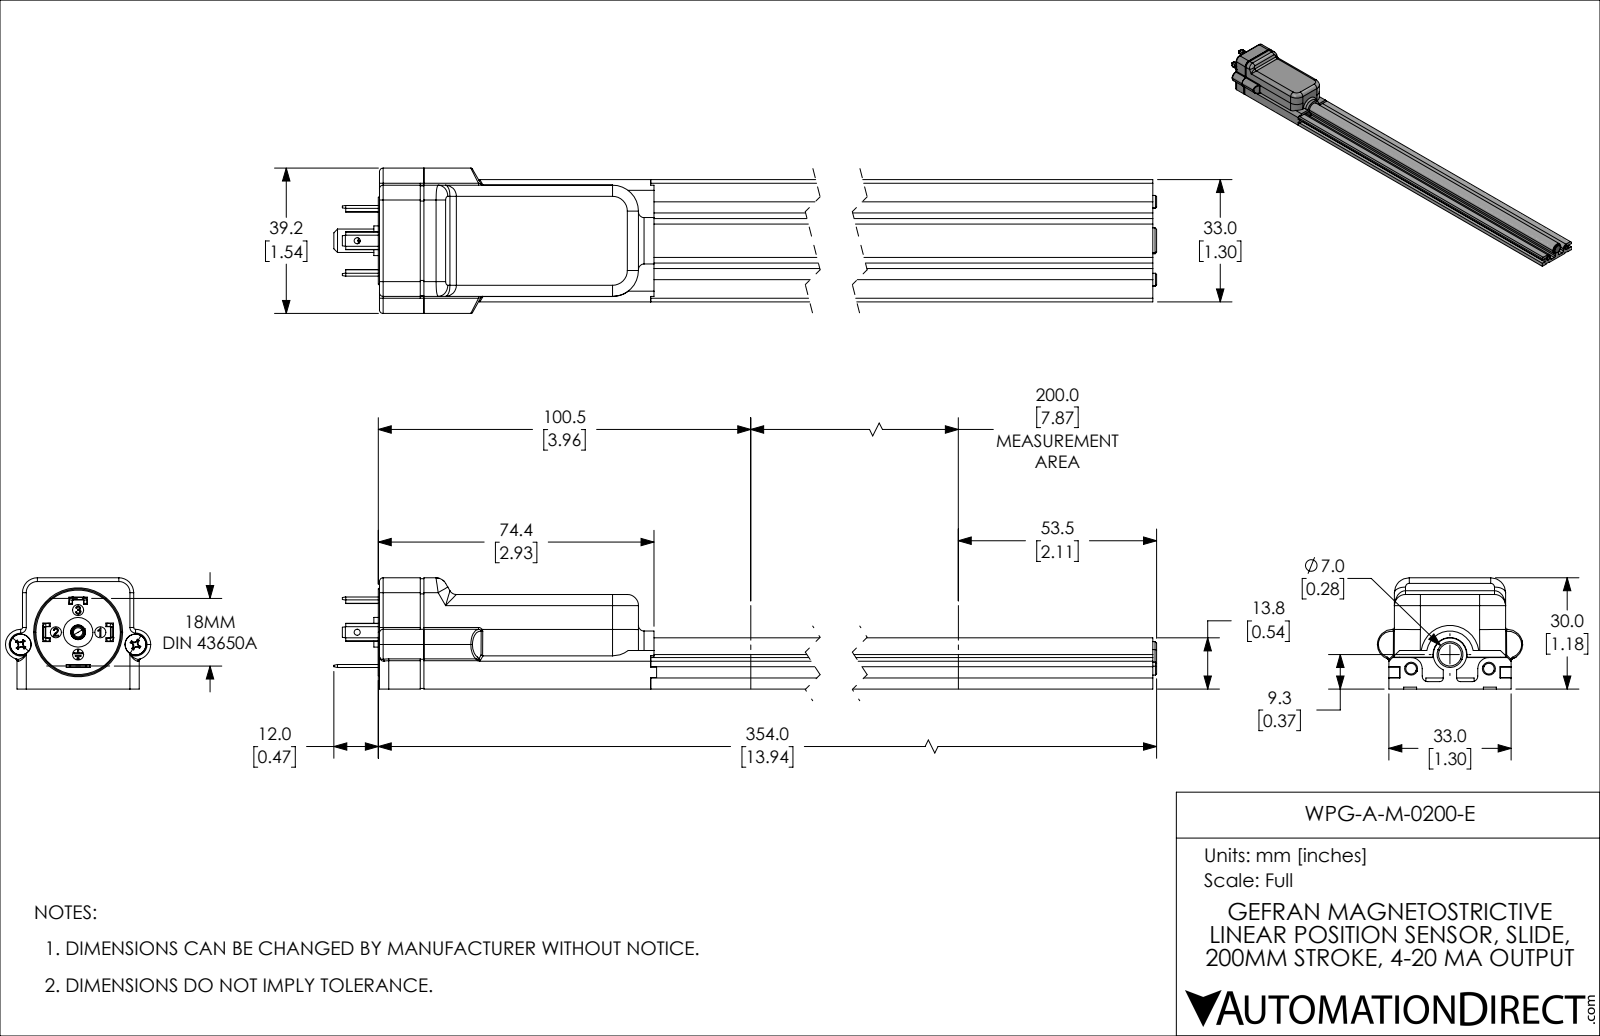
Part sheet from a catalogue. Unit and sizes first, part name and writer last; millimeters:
Units: millimetres
Overall size (bounding box): 366 × 39.2 × 30
Round holes (diameter × count): ⌀3 ×5, ⌀1.5 ×2, ⌀1.65 ×2, ⌀3.2 ×2, ⌀5.7 ×2, ⌀1.6 ×1, ⌀2.5 ×1, ⌀4 ×1
Round bosses / shafts (diameter × count): ⌀5.6 ×2, ⌀3.5 ×2, ⌀2.85 ×2, ⌀9 ×1, ⌀8 ×1, ⌀7 ×1, ⌀5.3 ×1, ⌀3.94 ×1
Partial cylindrical surfaces — rounded edges, fillets, slot ends (radius × count): R0.5 ×8, R3 ×8, R0.85 ×6, R1 ×5, R0.8 ×4, R1.5 ×4, R4.1 ×4, R7 ×4
Main face-to-face distances: 3, 1, 1.5, 2.5, 5.5, 6, 8.5, 30, 22.5, 0.5
Hole centre spacings: 6, 8.49, 10.06, 12, 12.3, 15.73, 15.85, 18.08
Volume: 124 954 mm³ · Surface area: 54 056 mm²
Bodies: 15 solids, 589 faces (371 planar, 139 cylindrical, 79 other)
Part name (STEP PRODUCT): WPG-A-M-0200-E
STEP written by: SolidWorks 2021 (CONFIG_CONTROL_DESIGN)
